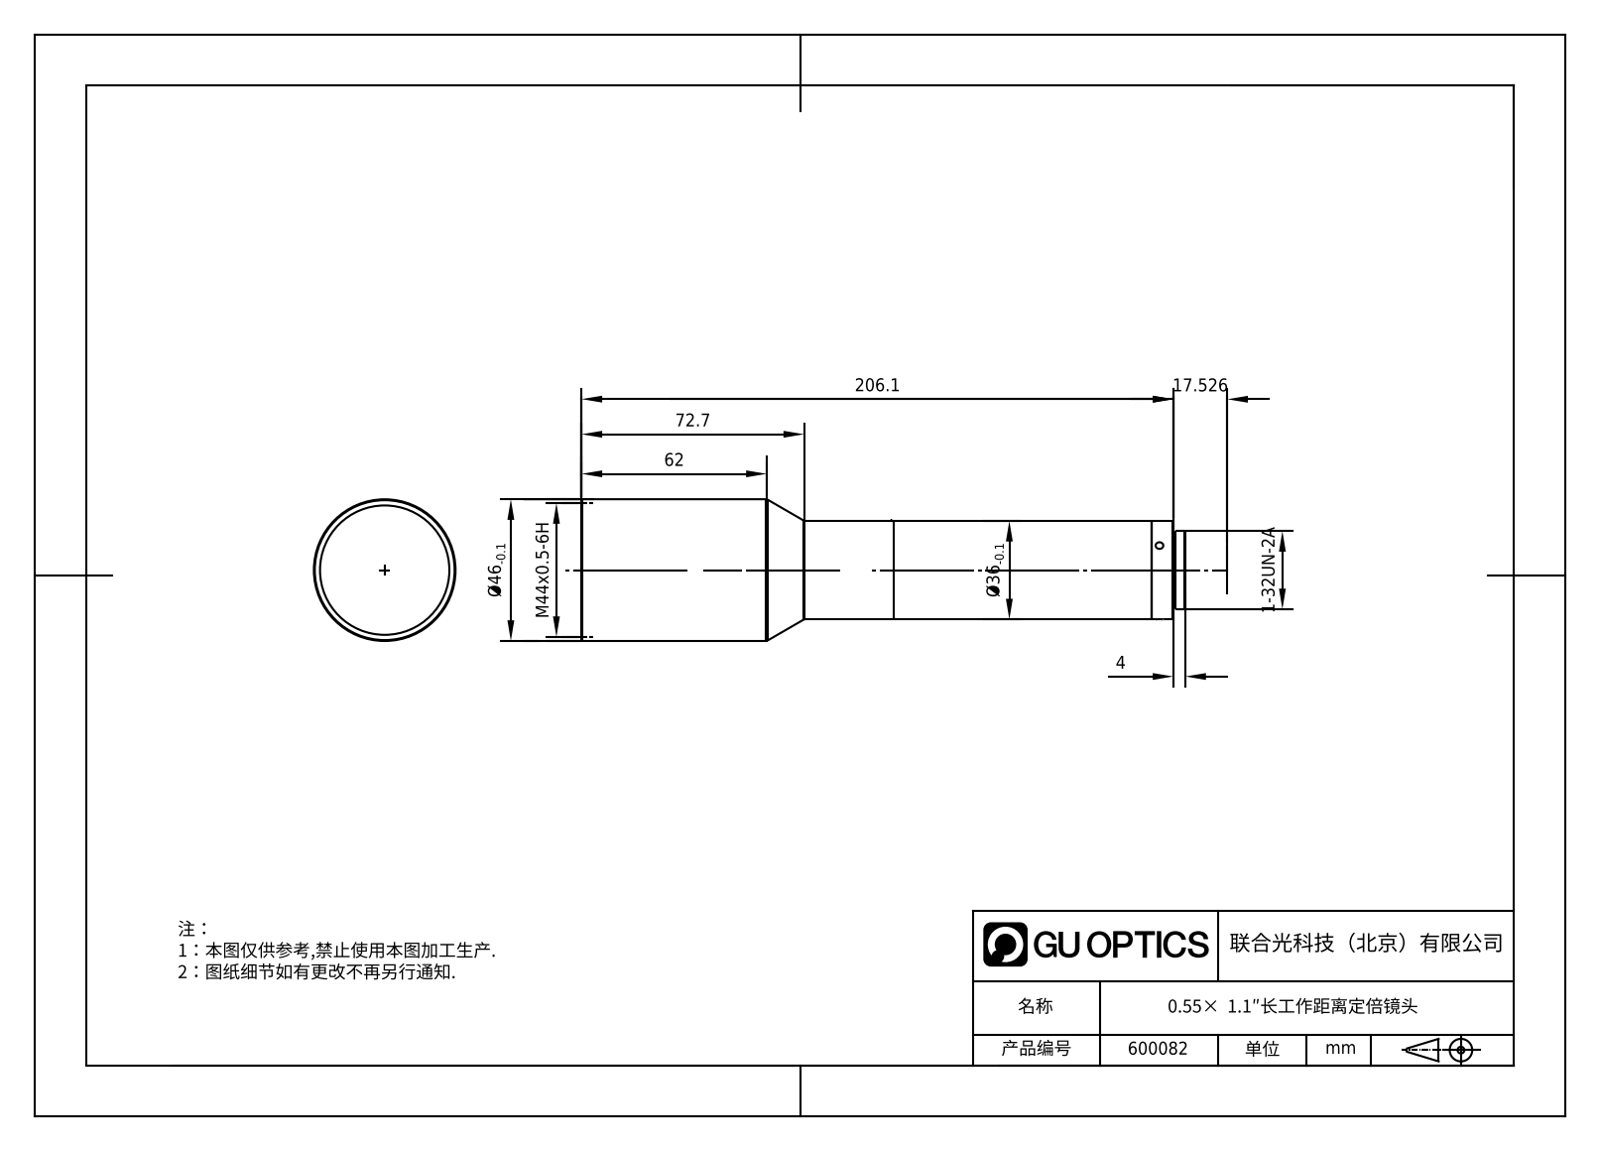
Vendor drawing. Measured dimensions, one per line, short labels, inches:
name: 600082
written by: SolidWorks 2020 (CONFIG_CONTROL_DESIGN)
unit: in
bodies: 2 solids, 27 faces (7 planar, 12 cylindrical, 8 other)
size: 8.271 × 1.811 × 1.811
volume: 15.19 in³; area: 51.04 in²
holes: 3× ⌀0.098, 1× ⌀1.654
bosses: 1× ⌀1.811, 1× ⌀1.417, 1× ⌀1, 1× ⌀0.969
rounds: 1× R0.666
face distances: 7.759, 0.157, 7.917, 8.271, 8.113, 0.354, 0.551, 0.394, 7.365, 7.72
